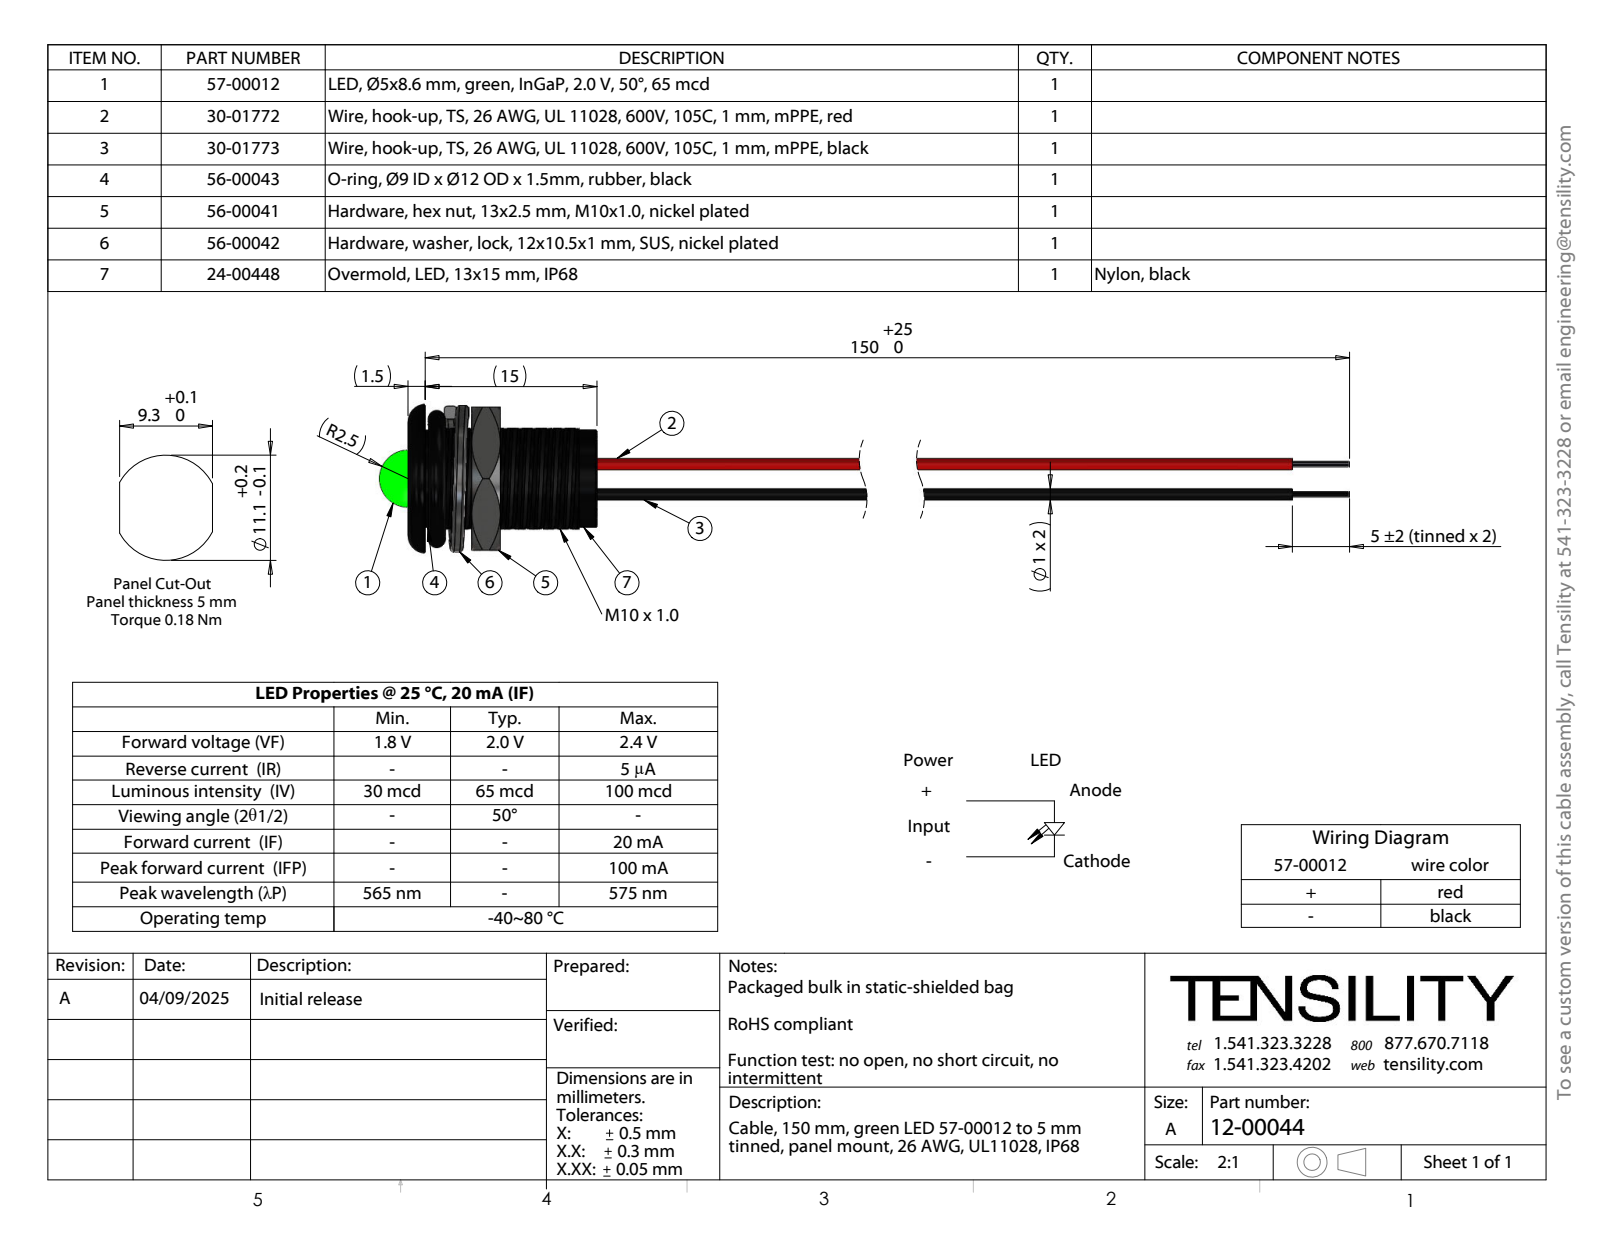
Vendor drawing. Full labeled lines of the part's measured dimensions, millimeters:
Part name (STEP PRODUCT): 56-00042_Split washer; 24-00448; 56-00041; 57-00012_trimmed leads (+4 more)
STEP written by: SolidWorks 2021 (CONFIG_CONTROL_DESIGN)
Units: millimetres
Bodies: 57 solids, 514 faces (185 planar, 246 cylindrical, 83 other)
Overall size (bounding box): 173.99 × 14.43 × 12.99
Volume: 1 769 mm³ · Surface area: 6 568 mm²
Round holes (diameter × count): ⌀1 ×2
Round bosses / shafts (diameter × count): ⌀1 ×2, ⌀0.83 ×2, ⌀8.5 ×1, ⌀5 ×1
Partial cylindrical surfaces — rounded edges, fillets, slot ends (radius × count): R4.33 ×1, R5 ×1
Main face-to-face distances: 1.5, 16.5, 15, 12.5, 8.06, 6.56, 8.44, 5.56, 4.06, 2.5
Hole centre spacings: 0.36, 0.38, 0.33, 2.43, 2.35, 2.48, 2.52, 2.56
